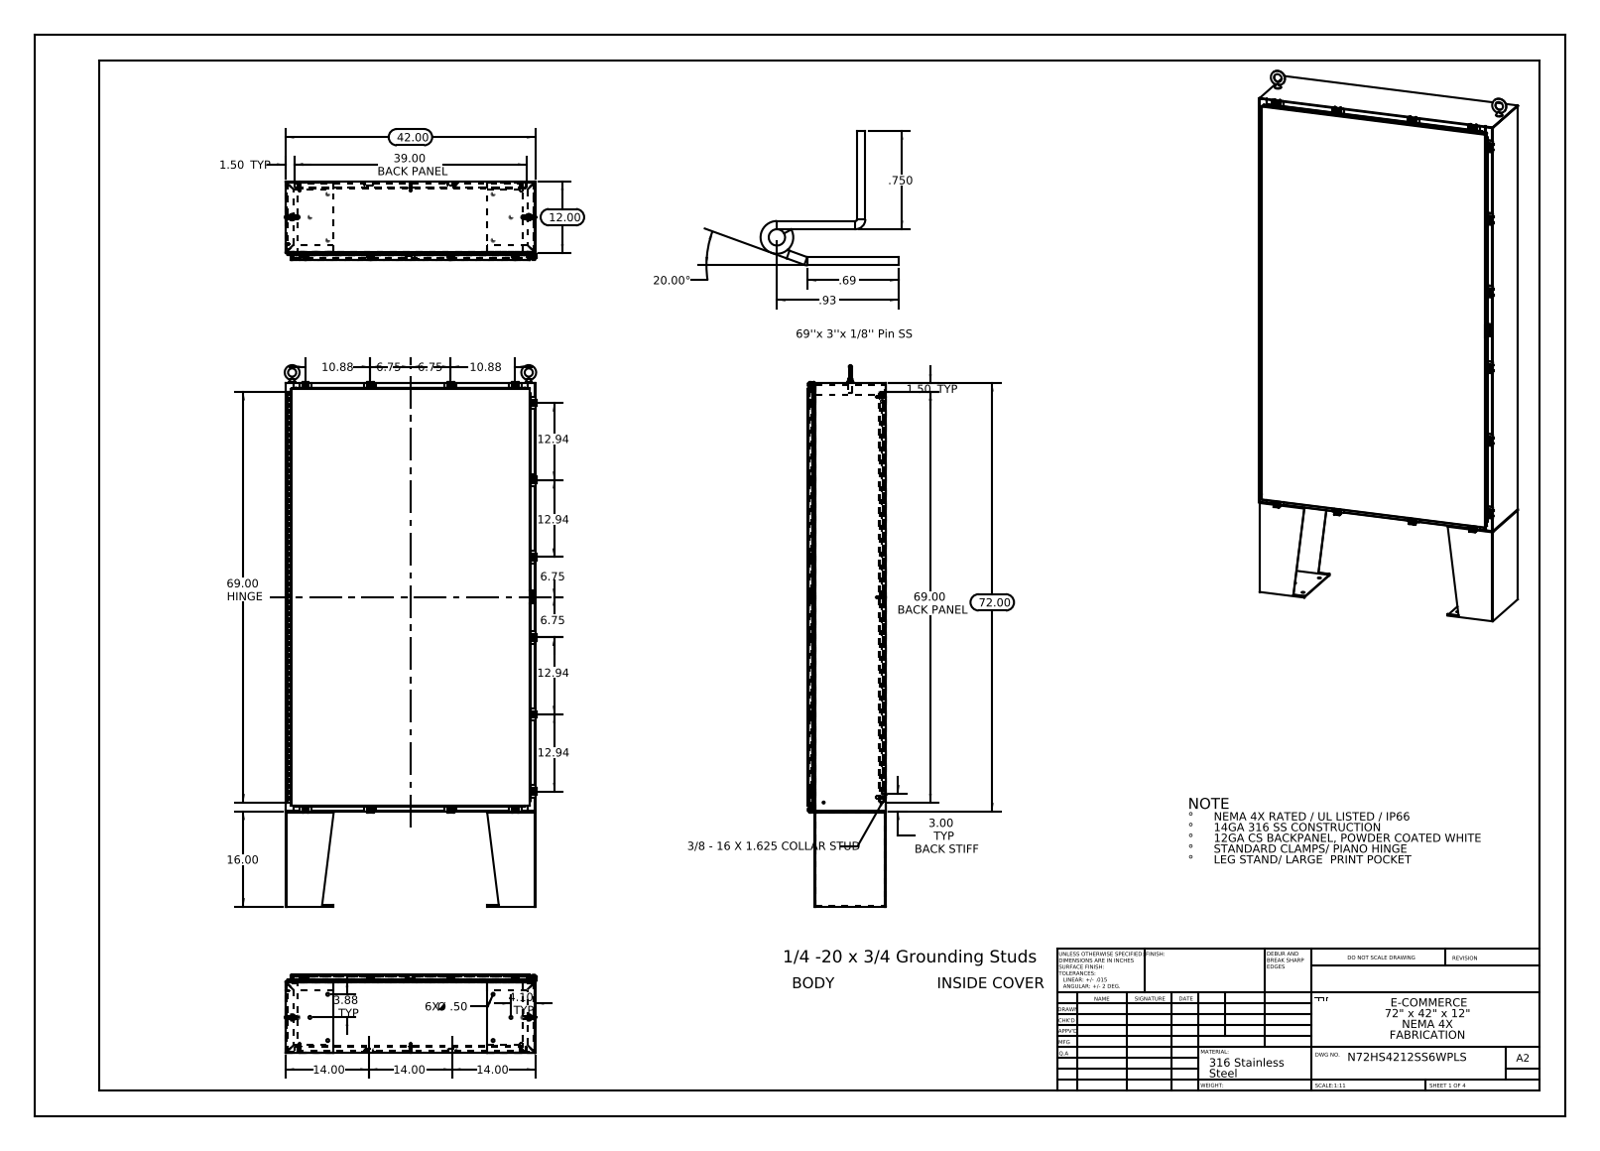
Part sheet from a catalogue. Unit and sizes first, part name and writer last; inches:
Units: inches
Overall size (bounding box): 91 × 42.346 × 13.201
Round holes (diameter × count): ⌀0.213 ×14, ⌀0.26 ×14, ⌀0.5 ×14, ⌀0.25 ×8, ⌀0.75 ×4, ⌀0.125 ×2, ⌀0.125 ×1
Round bosses / shafts (diameter × count): ⌀0.25 ×15, ⌀0.5 ×14, ⌀0.399 ×14, ⌀0.625 ×10, ⌀0.375 ×8, ⌀0.33 ×8, ⌀0.157 ×8, ⌀0.14 ×8
Partial cylindrical surfaces — rounded edges, fillets, slot ends (radius × count): R0.06 ×62, R0.013 ×39, R0.088 ×33, R0.12 ×28, R0.141 ×28, R0.05 ×25, R0.145 ×24, R0.08 ×20
Main face-to-face distances: 0.075, 13.126, 0.104, 13.051, 1.075, 13.201, 12.126, 1, 12.051, 1.179
Hole centre spacings: 7.069, 2.225, 7.137, 31.035, 33.625, 34.004, 34.006, 35.74
Volume: 1 189 in³ · Surface area: 28 746 in²
Bodies: 108 solids, 4313 faces (2196 planar, 1809 cylindrical, 308 other)
Part name (STEP PRODUCT): N72HS4212SSWPLS Padlock Hasp; N72HS4212SSWPLS Bottom; N72HS4212SSWPLS 22101002; N72HS4212SSWPLS Hinge Enclosure Side2 (+8 more)
STEP written by: SolidWorks 2013 (CONFIG_CONTROL_DESIGN)
